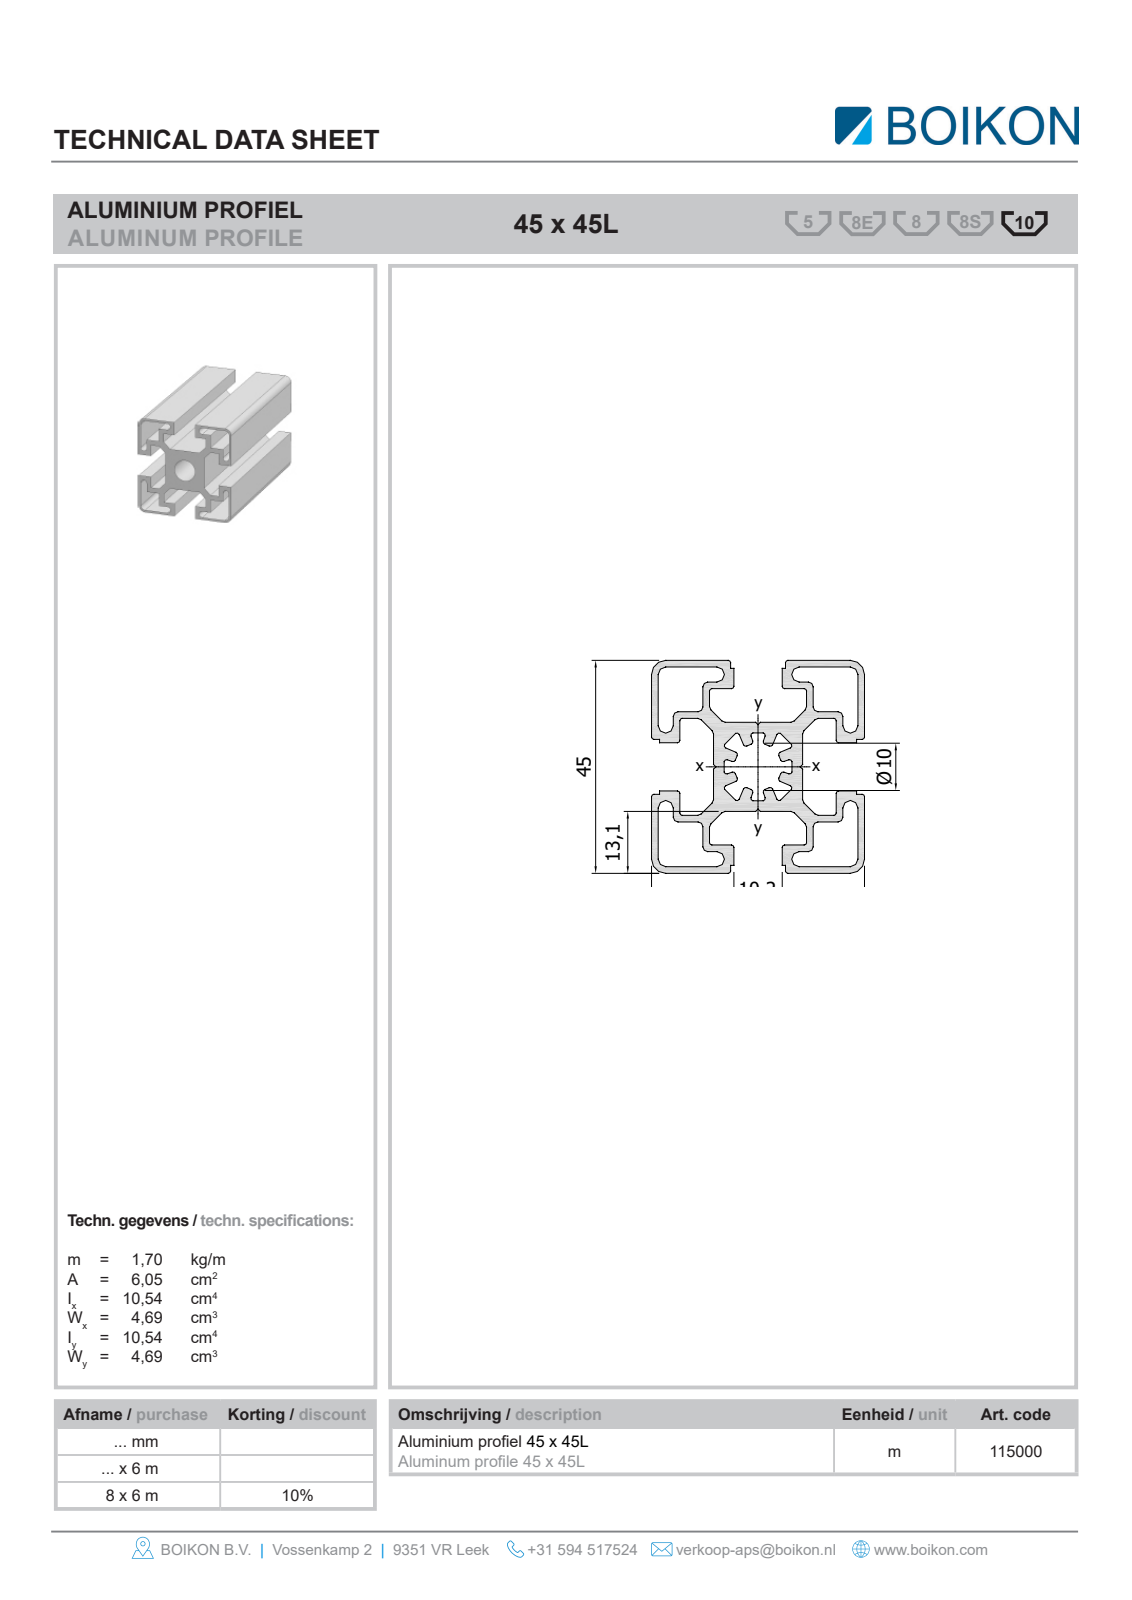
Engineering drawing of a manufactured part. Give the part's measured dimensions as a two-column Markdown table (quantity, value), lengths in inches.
| quantity | value |
| --- | --- |
| part name | Root; 11500045x45LBOIKON0 |
| STEP written by | HiCAD 2013 1802.4 Build 509 (AUTOMOTIVE_DESIGN) |
| units | inches |
| bodies | 1 solid, 71 faces (62 planar, 9 cylindrical, 0 other) |
| overall size | 39.37 × 1.772 × 1.772 |
| volume | 50.63 in³ |
| surface area | 807.8 in² |
| round holes (diameter × count) | 0.394 × 1 |
| partial cylindrical surfaces (radius × count) | 0.079 × 4, 0.118 × 4 |
| main face-to-face distances | 0.394, 1.378, 1.772, 0.516, 1.256, 0.122, 0.862, 0.039, 1.732, 0.354 |
